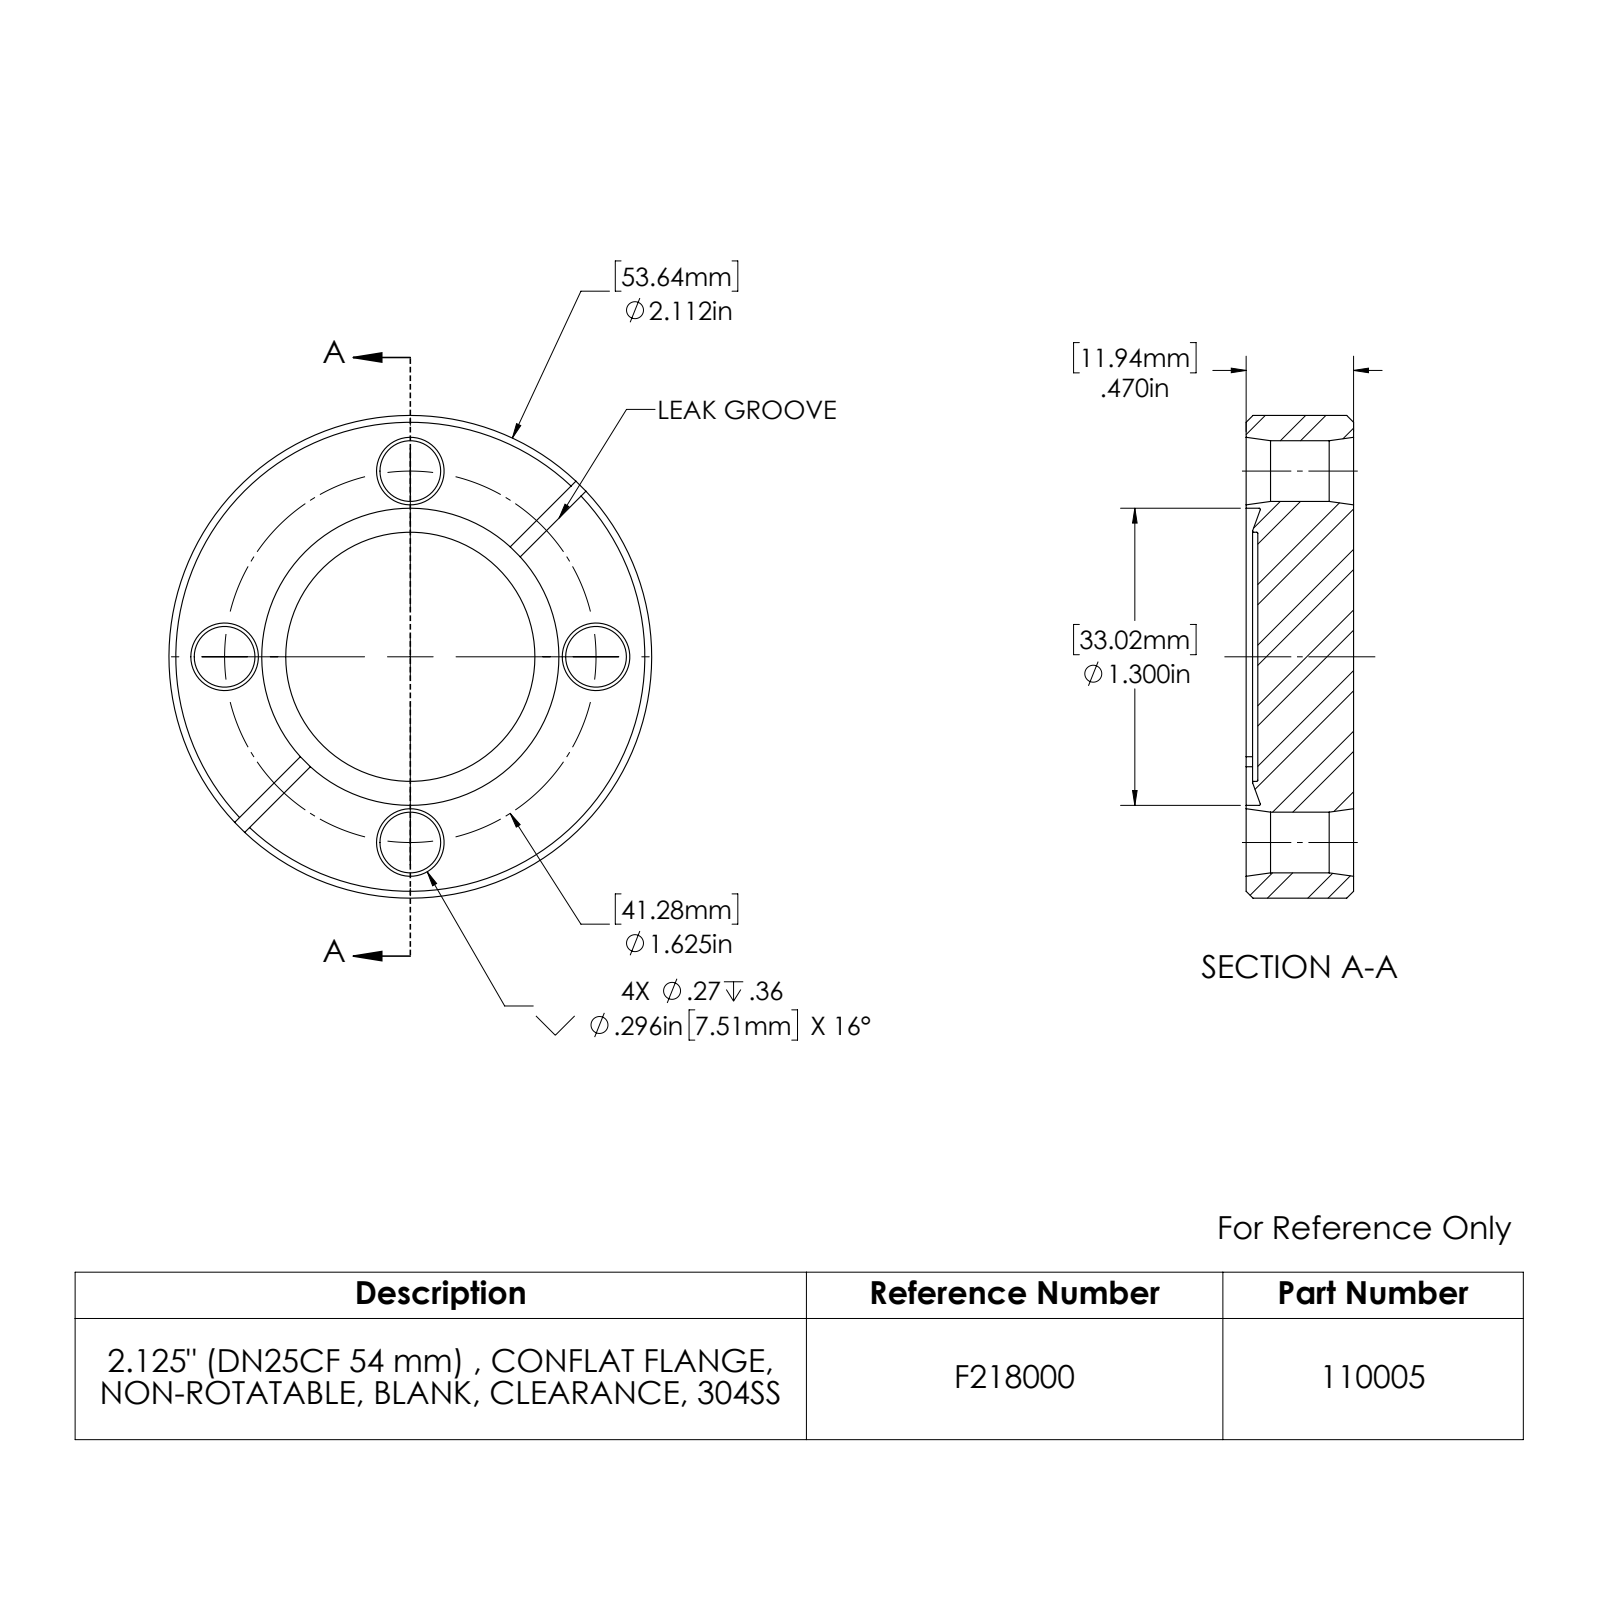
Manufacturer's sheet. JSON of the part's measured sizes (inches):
{"part_name": "110005", "step_written_by": "SolidWorks 2022 (AUTOMOTIVE_DESIGN)", "units": "inches", "bodies": {"solids": 1, "faces": 53, "planar": 8, "cylindrical": 16, "other": 29}, "overall_size": [2.112, 2.112, 0.47], "volume_in3": 1.46, "surface_area_in2": 11.44, "round_holes": [[0.266, 4], [1.09, 1], [1.3, 1]], "round_bosses_or_shafts": [[2.112, 1]], "partial_cylinders_radius": [[1.25, 2]], "face_to_face_distances": [0.47, 0.051, 0.419, 0.062], "hole_center_spacings": [0.813, 1.149, 1.625]}
